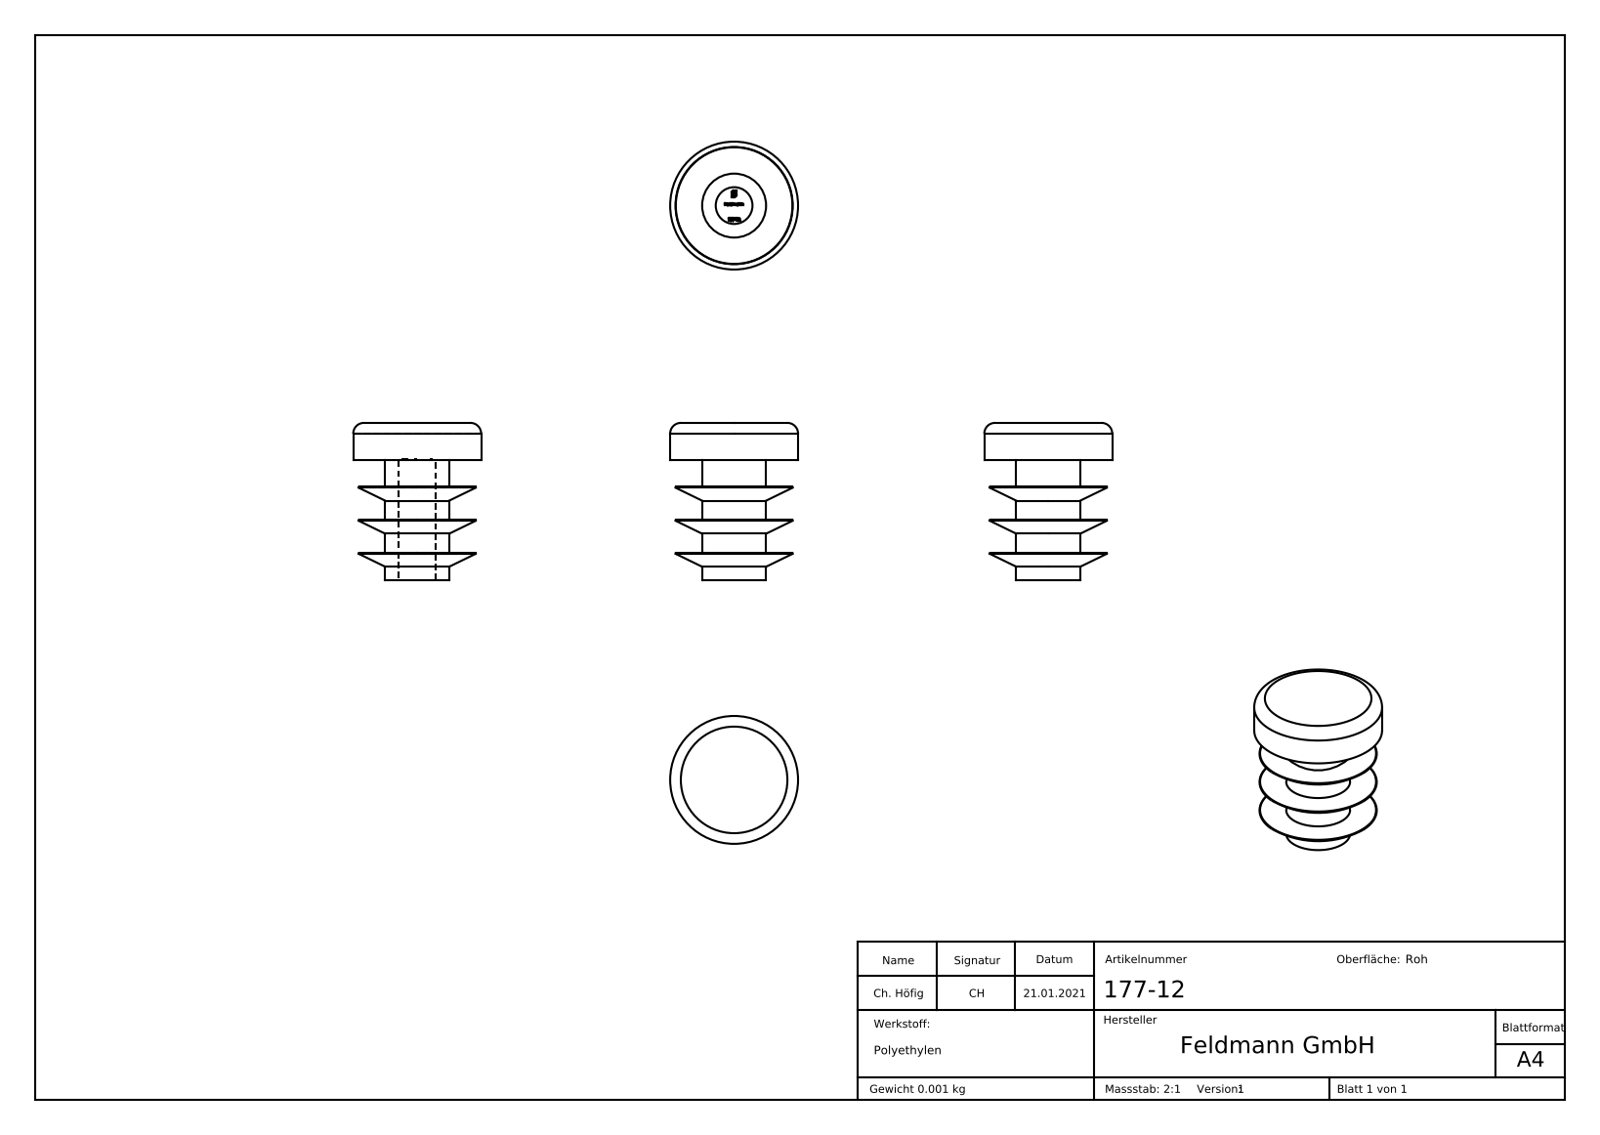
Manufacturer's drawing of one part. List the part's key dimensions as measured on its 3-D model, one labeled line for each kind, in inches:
Part name (STEP PRODUCT): 177-12
STEP written by: SolidWorks 2018 (CONFIG_CONTROL_DESIGN)
Units: inches
Bodies: 1 solid, 220 faces (133 planar, 6 cylindrical, 81 other)
Overall size (bounding box): 0.583 × 0.472 × 0.472
Volume: 0.044 in³ · Surface area: 1.603 in²
Round holes (diameter × count): ⌀0.136 ×1
Round bosses / shafts (diameter × count): ⌀0.472 ×1, ⌀0.236 ×1
Main face-to-face distances: 0.122, 0.138, 0.22, 0.358, 0.098, 0.236, 0.244, 0.343, 0.48, 0.102
